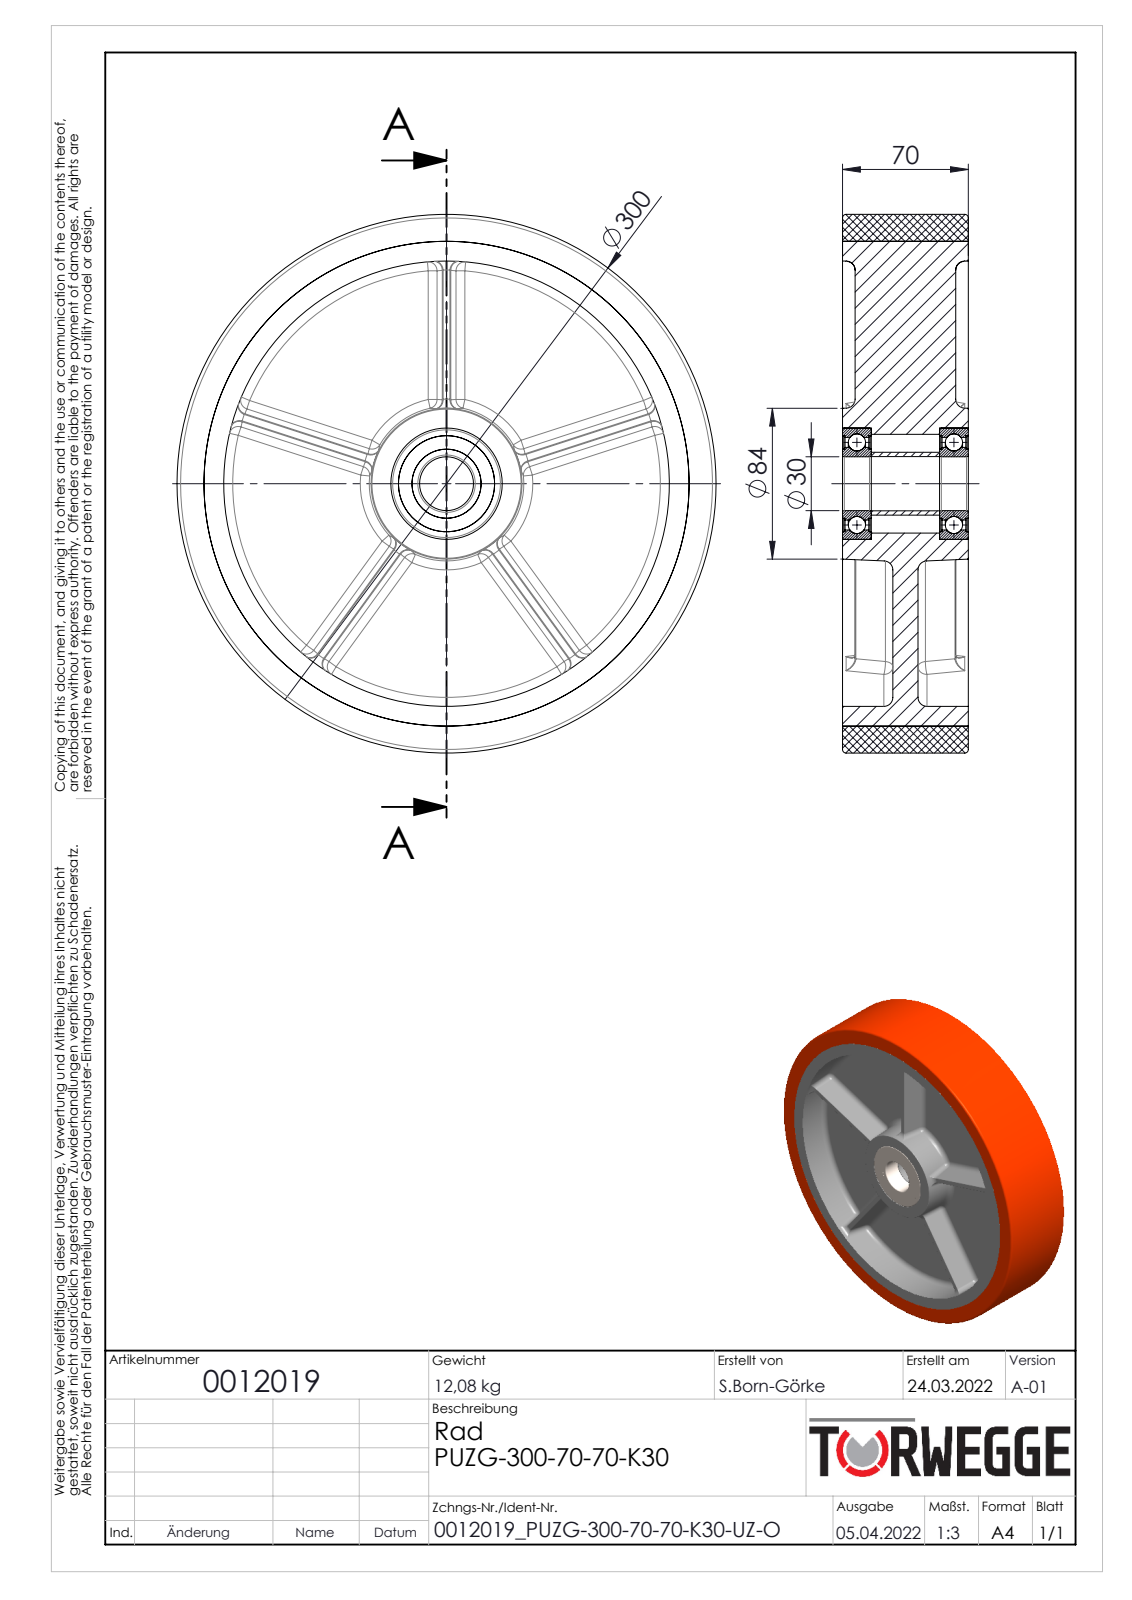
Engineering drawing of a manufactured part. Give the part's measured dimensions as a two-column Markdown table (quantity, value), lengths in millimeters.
| quantity | value |
| --- | --- |
| part name | 0012019 |
| STEP written by | SolidWorks 2020 (AUTOMOTIVE_DESIGN) |
| units | millimeters |
| bodies | 13 solids, 446 faces (74 planar, 116 cylindrical, 256 other) |
| overall size | 300 × 300 × 70 |
| volume | 2 609 000 mm³ |
| surface area | 458 691 mm² |
| round holes (diameter × count) | 30 × 1, 30.2 × 1, 38.48 × 1, 51.57 × 1, 53.52 × 1, 55 × 1, 62 × 1, 248 × 1, 270 × 1 |
| round bosses / shafts (diameter × count) | 300 × 1, 40.43 × 1, 35 × 1 |
| partial cylindrical surfaces (radius × count) | 0.5 × 20, 5 × 20 |
| main face-to-face distances | 28, 42, 14, 70, 54, 14.26, 16, 12, 26, 14.25 |
